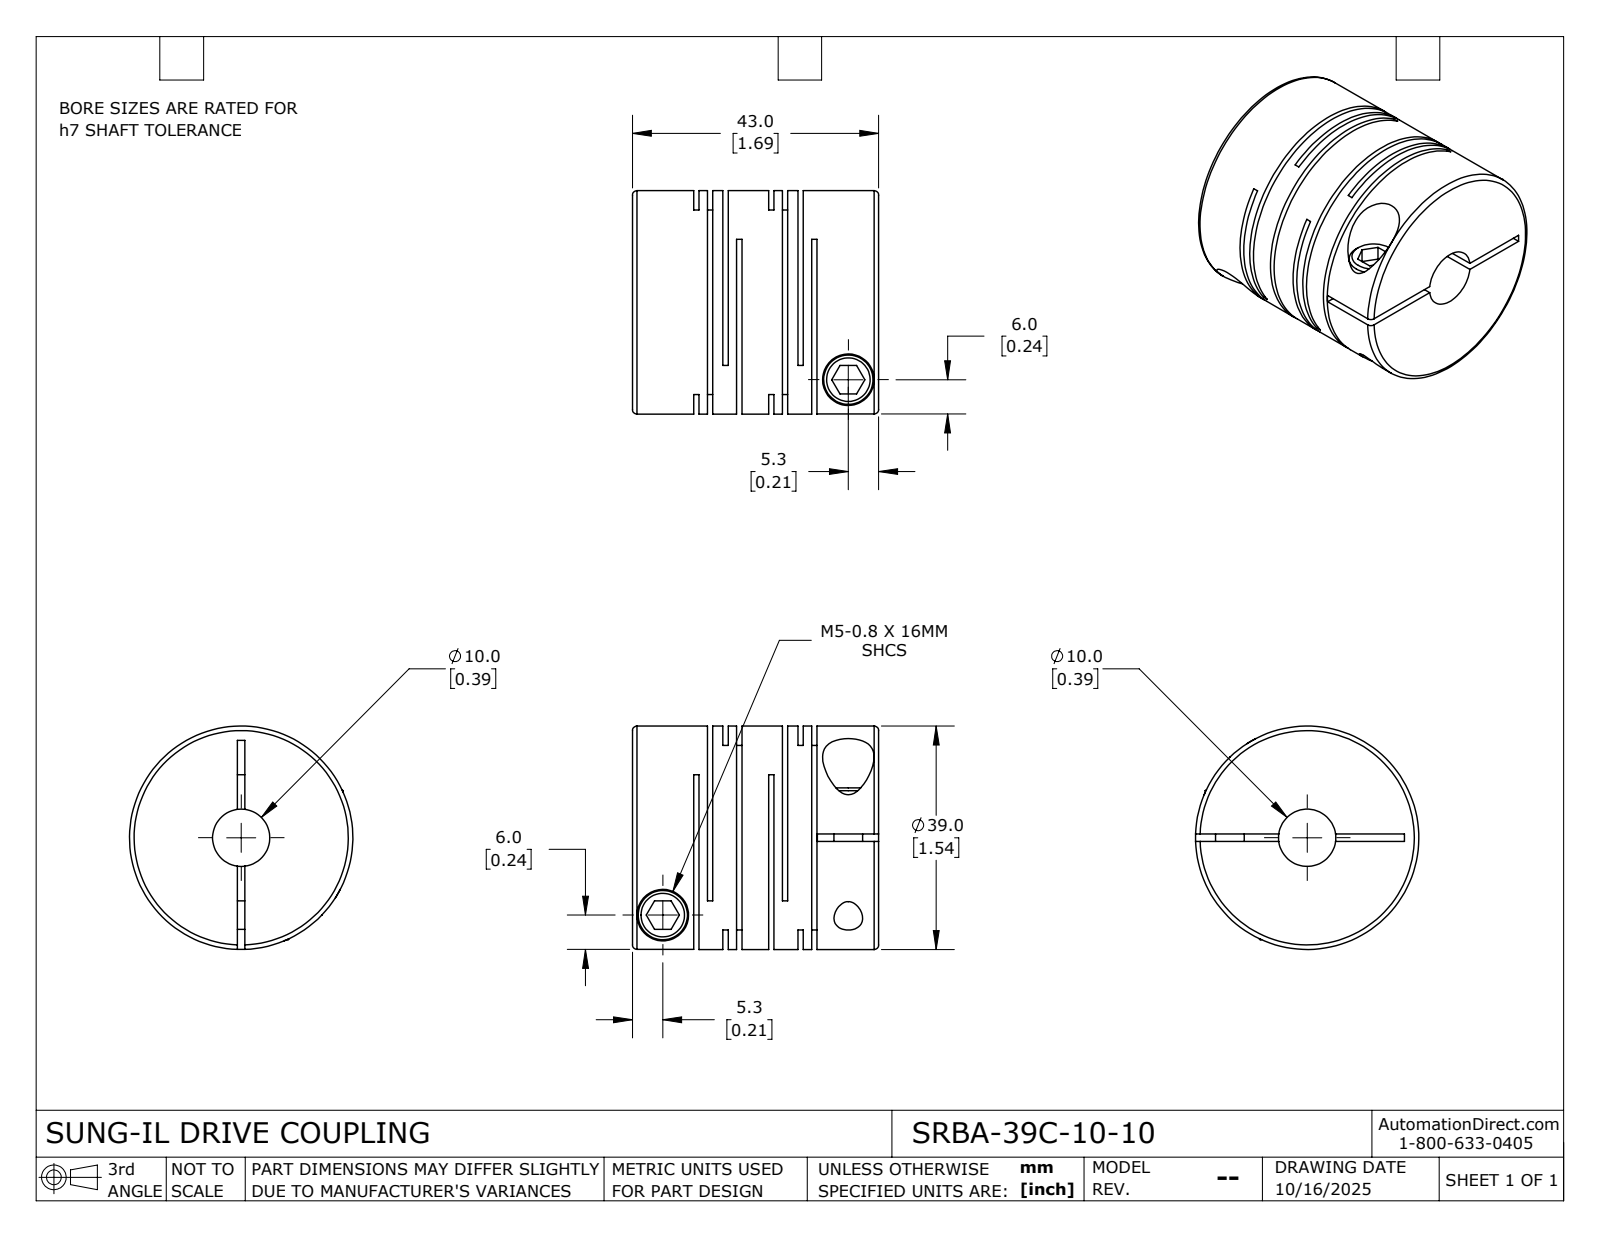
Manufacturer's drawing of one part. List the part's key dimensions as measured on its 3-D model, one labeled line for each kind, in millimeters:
Part name (STEP PRODUCT): SRBA-39C-10-10
STEP written by: SolidWorks 2024 (CONFIG_CONTROL_DESIGN)
Units: millimetres
Bodies: 1 solid, 115 faces (60 planar, 42 cylindrical, 13 other)
Overall size (bounding box): 43 × 39 × 39
Volume: 39 562 mm³ · Surface area: 24 723 mm²
Round holes (diameter × count): ⌀5 ×2, ⌀9 ×2, ⌀10 ×1
Round bosses / shafts (diameter × count): ⌀8.6 ×2, ⌀39 ×1
Main face-to-face distances: 13.1, 0.92, 2.4, 5.1, 10.7, 14.02, 18.2, 12.18, 1.48, 4.18
